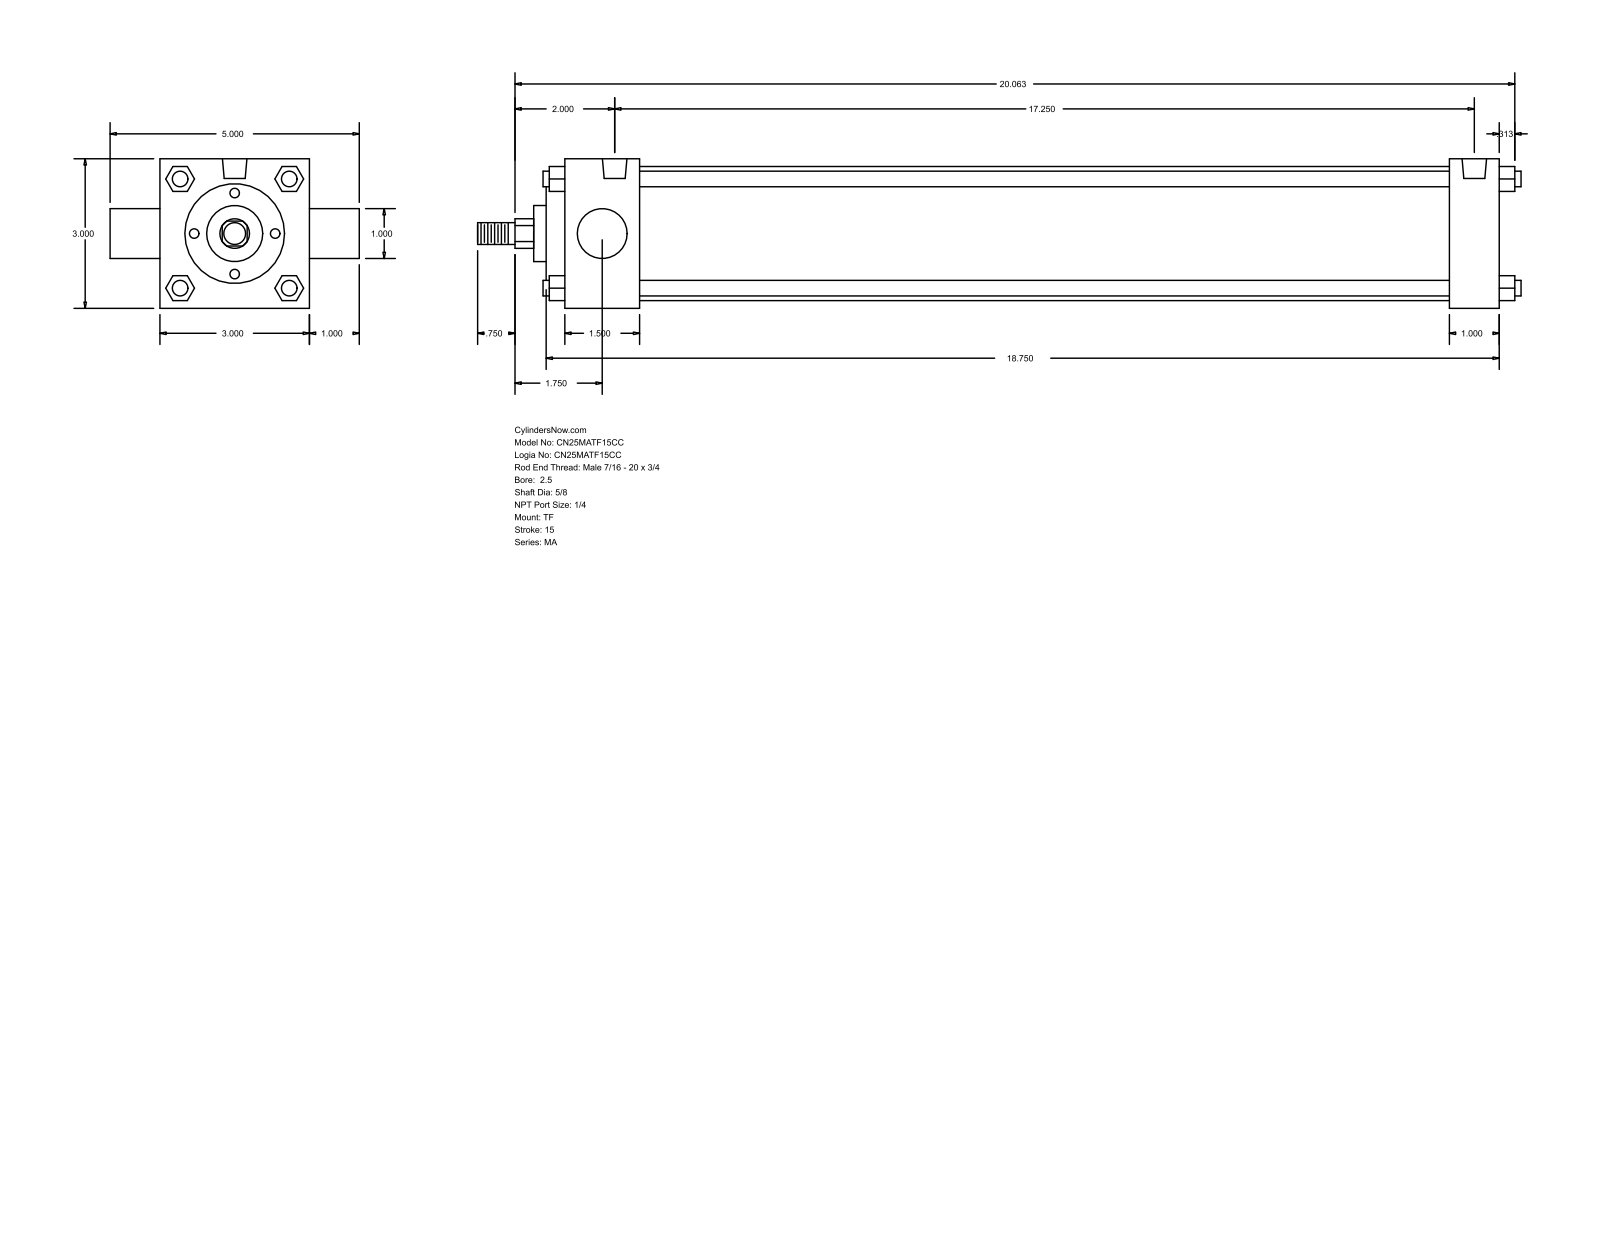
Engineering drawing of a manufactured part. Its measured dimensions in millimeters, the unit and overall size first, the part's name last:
Units: millimetres
Overall size (bounding box): 531.81 × 127 × 76.2
Round holes (diameter × count): ⌀7.94 ×3, ⌀12.49 ×2
Round bosses / shafts (diameter × count): ⌀7.94 ×4, ⌀68.33 ×1, ⌀50.8 ×1, ⌀28.57 ×1, ⌀25.4 ×1, ⌀15.88 ×1, ⌀11.11 ×1
Partial cylindrical surfaces — rounded edges, fillets, slot ends (radius × count): R7.54 ×1
Main face-to-face distances: 76.2, 476.25, 25.4, 38.1, 450.85, 412.75, 438.15, 12.7, 9.52, 47.62
Hole centre spacings: 438.15
Bodies: 0 solids, 122 faces (93 planar, 29 cylindrical, 0 other)
Part name (STEP PRODUCT): MA_TF__0250_0.625
STEP written by: GSSL Pune (CONFIG_CONTROL_DESIGN)
